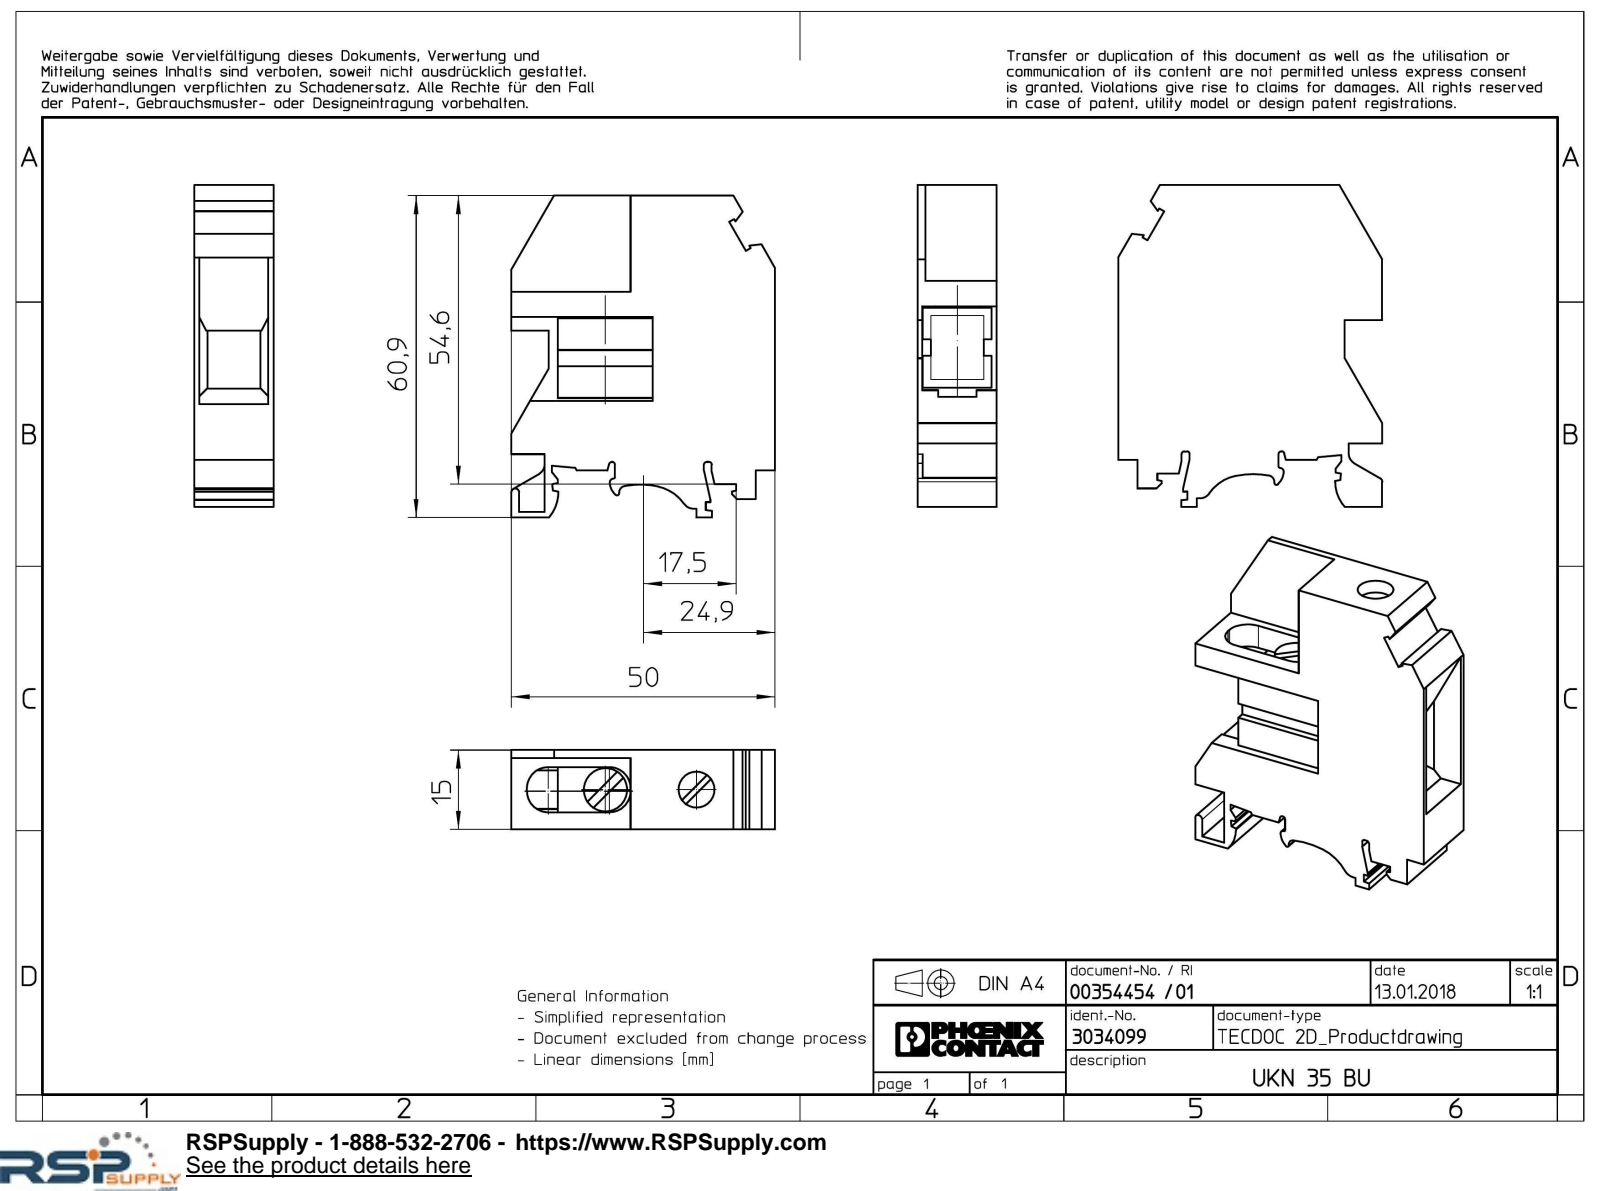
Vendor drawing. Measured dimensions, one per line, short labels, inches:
name: UKN_35_BU-select
written by: Creo Elements/Direct Modeling 18.1I 14-Aug-2016 (C) Parametric Technology GmbH (AUTOMOTIVE_DESIGN)
unit: in
bodies: 1 solid, 139 faces (116 planar, 23 cylindrical, 0 other)
size: 2.398 × 1.969 × 0.591
volume: 1.639 in³; area: 19.11 in²
holes: 1× ⌀0.268
bosses: 1× ⌀0.323
rounds: 4× R0.02, 4× R0.157, 2× R0.079, 1× R0.012, 1× R0.016, 1× R0.028, 1× R0.03, 1× R0.047
face distances: 0.591, 0.531, 0.039, 0.551, 0.059, 0.492, 0.033, 0.026, 0.557, 0.02
